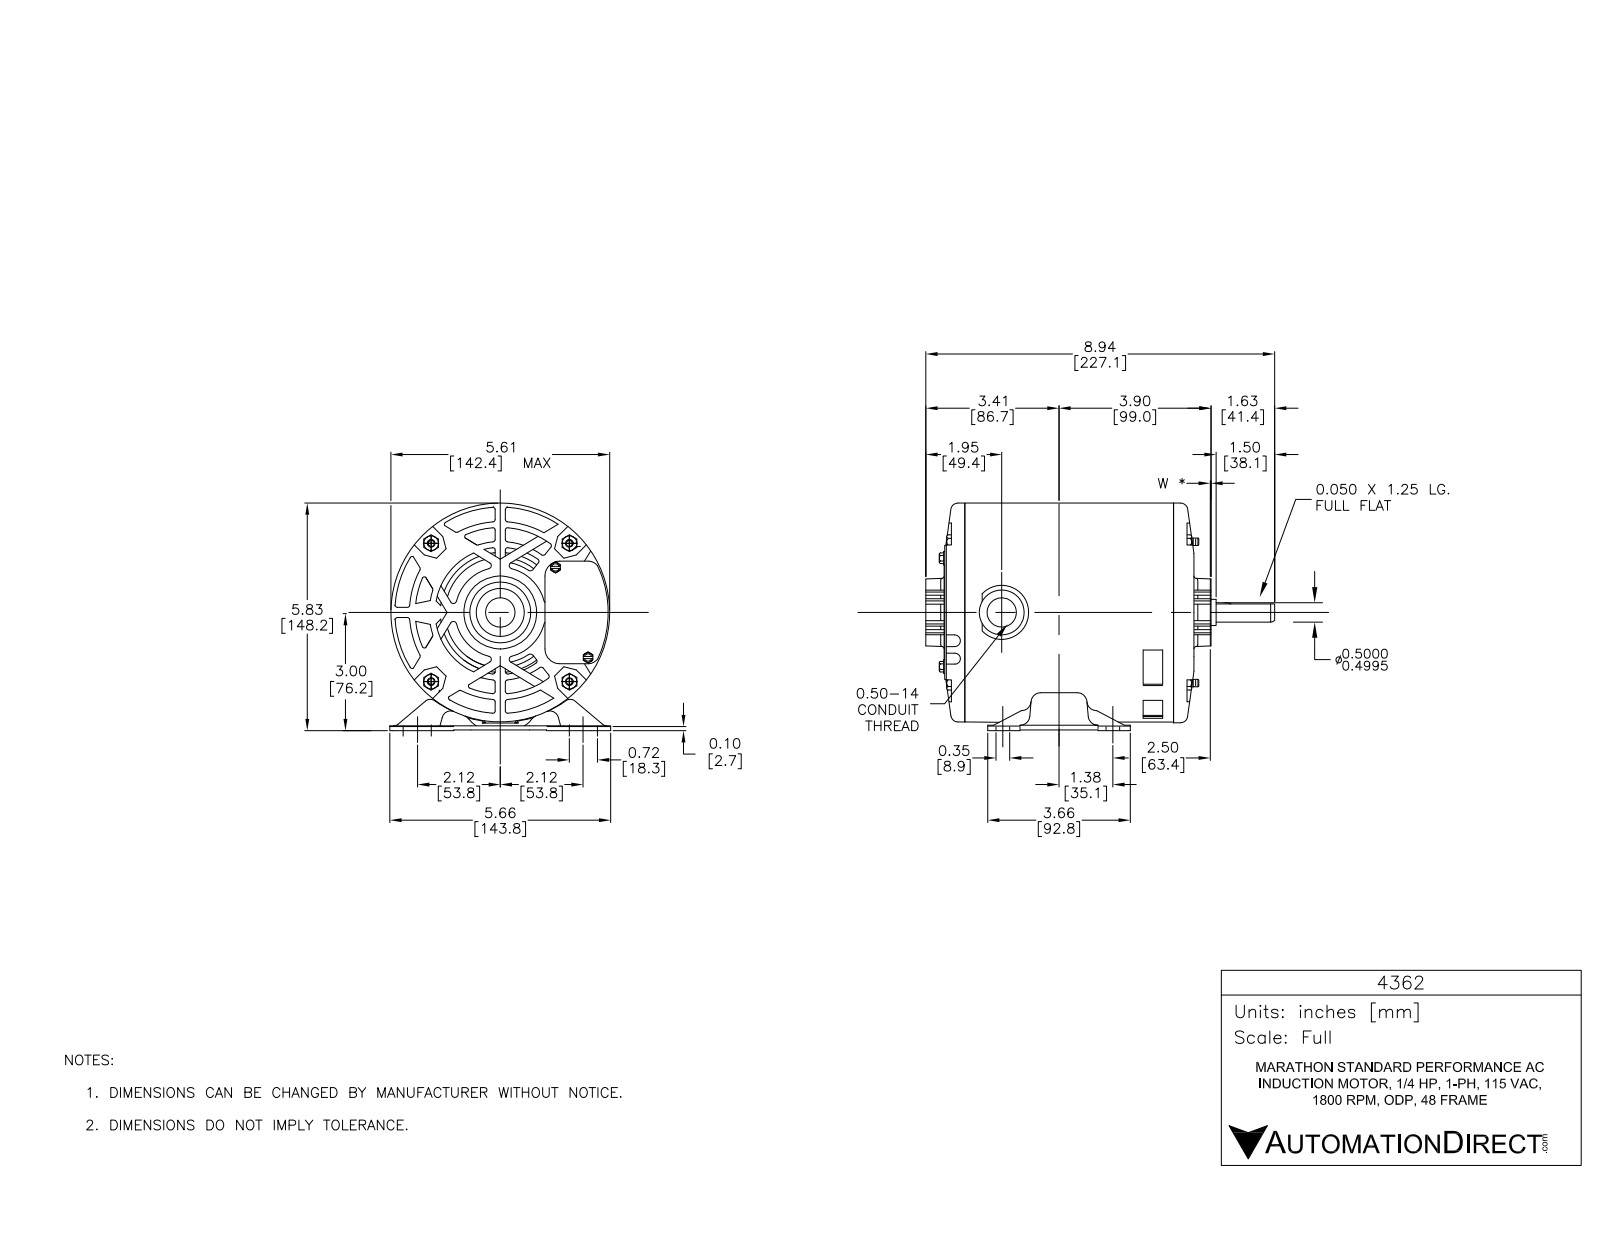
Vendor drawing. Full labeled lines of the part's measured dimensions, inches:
Part name (STEP PRODUCT): 4354 1st b2
STEP written by: SolidWorks 2017 (AUTOMOTIVE_DESIGN)
Units: inches
Bodies: 17 solids, 3315 faces (1095 planar, 629 cylindrical, 1591 other)
Overall size (bounding box): 8.94 × 5.78 × 5.78
Volume: 21.97 in³ · Surface area: 439.9 in²
Round holes (diameter × count): ⌀0.153 ×11, ⌀0.38 ×6, ⌀0.25 ×5, ⌀0.193 ×4, ⌀0.218 ×2, ⌀0.457 ×1, ⌀0.505 ×1, ⌀0.64 ×1, ⌀0.669 ×1, ⌀0.687 ×1, ⌀0.73 ×1, ⌀0.747 ×1
Round bosses / shafts (diameter × count): ⌀0.19 ×4, ⌀0.166 ×4, ⌀0.399 ×3, ⌀0.335 ×2, ⌀0.164 ×2, ⌀5.62 ×1, ⌀5.615 ×1, ⌀5.498 ×1
Partial cylindrical surfaces — rounded edges, fillets, slot ends (radius × count): R0.06 ×52, R0.03 ×44, R0.02 ×27, R0.01 ×24, R0.015 ×24, R0.05 ×16, R0.12 ×15, R0.25 ×10
Main face-to-face distances: 0.04, 6.01, 0.105, 6.05, 0.06, 0.08, 0.025, 0.13, 0.104, 0.025
Hole centre spacings: 2.562, 3.624, 1.12, 1.19, 2.4, 2.578, 4.243, 4.82
